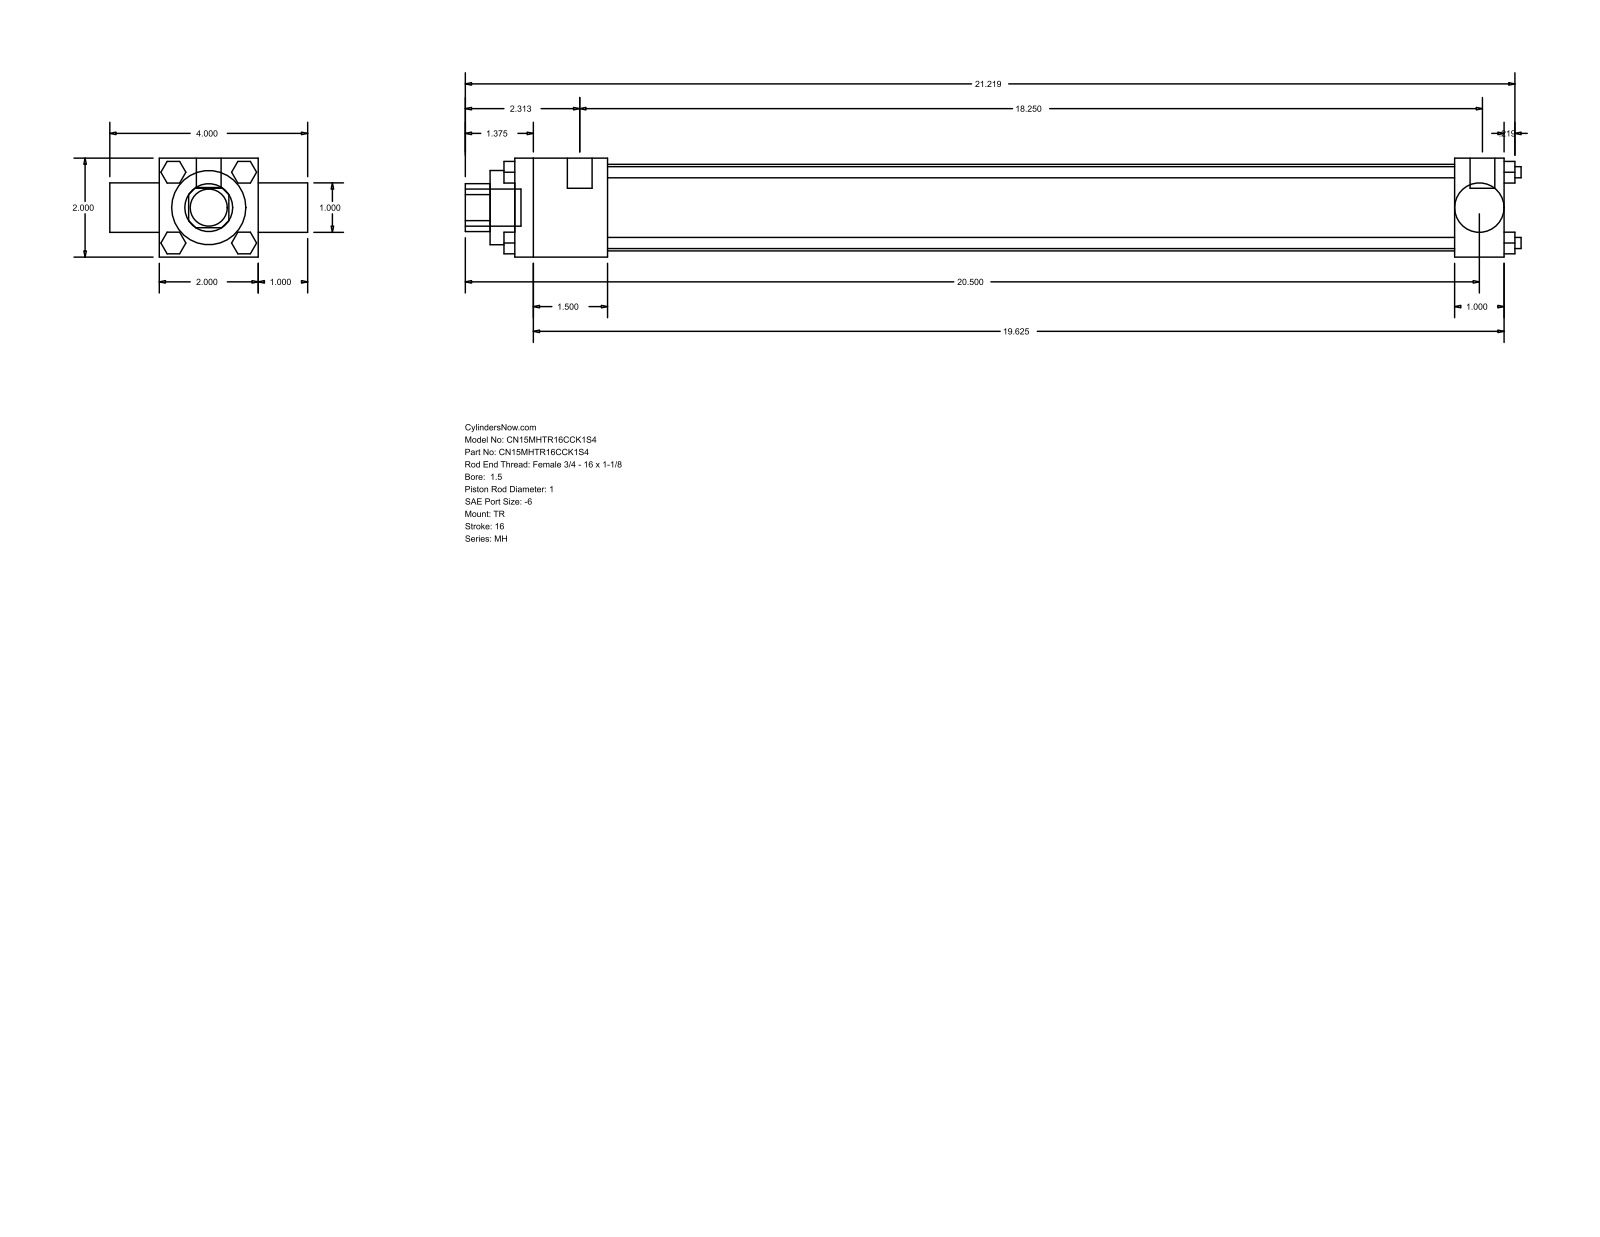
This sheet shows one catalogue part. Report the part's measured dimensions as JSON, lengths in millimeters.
{"part_name": "MH_TR__0150_1", "step_written_by": "GSSL Pune (CONFIG_CONTROL_DESIGN)", "units": "millimeters", "bodies": {"solids": 0, "faces": 120, "planar": 92, "cylindrical": 28, "other": 0}, "overall_size": [542.13, 101.6, 50.8], "round_holes": [[25.35, 1], [25.4, 1], [38.1, 1], [44.45, 1]], "round_bosses_or_shafts": [[5.71, 4], [5.56, 3], [12.7, 2], [19.05, 1]], "partial_cylinders_radius": [[12.29, 1]], "face_to_face_distances": [50.8, 25.4, 508, 76.2, 47.63, 460.37, 482.6, 434.97, 513.56, 12.7]}
